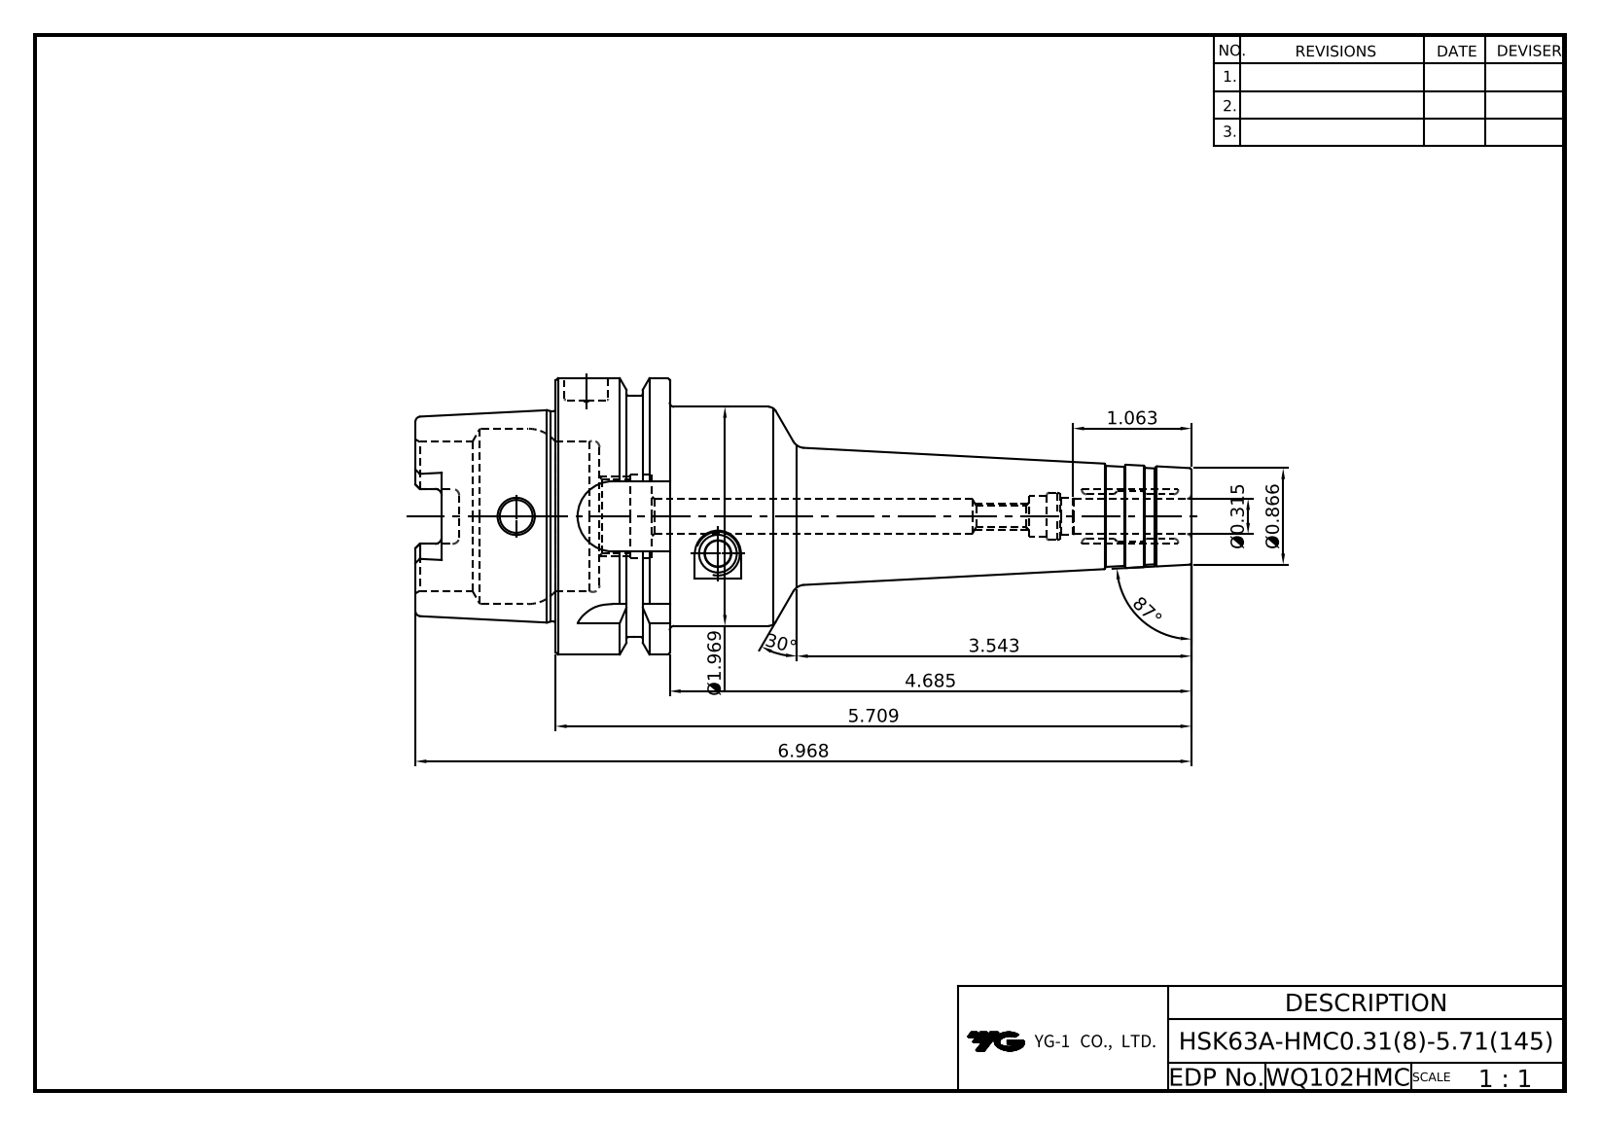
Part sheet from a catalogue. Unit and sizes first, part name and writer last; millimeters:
Units: millimetres
Overall size (bounding box): 177 × 63 × 63
Round holes (diameter × count): ⌀4.92 ×1, ⌀7.5 ×1, ⌀8 ×1, ⌀8.6 ×1, ⌀10 ×1, ⌀16.92 ×1, ⌀19 ×1, ⌀34 ×1, ⌀40 ×1
Round bosses / shafts (diameter × count): ⌀63 ×1, ⌀55 ×1, ⌀50 ×1, ⌀48.04 ×1
Partial cylindrical surfaces — rounded edges, fillets, slot ends (radius × count): R1.5 ×6, R2.88 ×4, R8 ×4
Main face-to-face distances: 26, 10, 16, 32, 42, 58, 4, 53, 22, 177
Volume: 180 161 mm³ · Surface area: 36 187 mm²
Bodies: 1 solid, 136 faces (42 planar, 34 cylindrical, 60 other)
Part name (STEP PRODUCT): LO-HSK63A-HMC8-145
STEP written by: Autodesk Inventor 2020 (AUTOMOTIVE_DESIGN)
